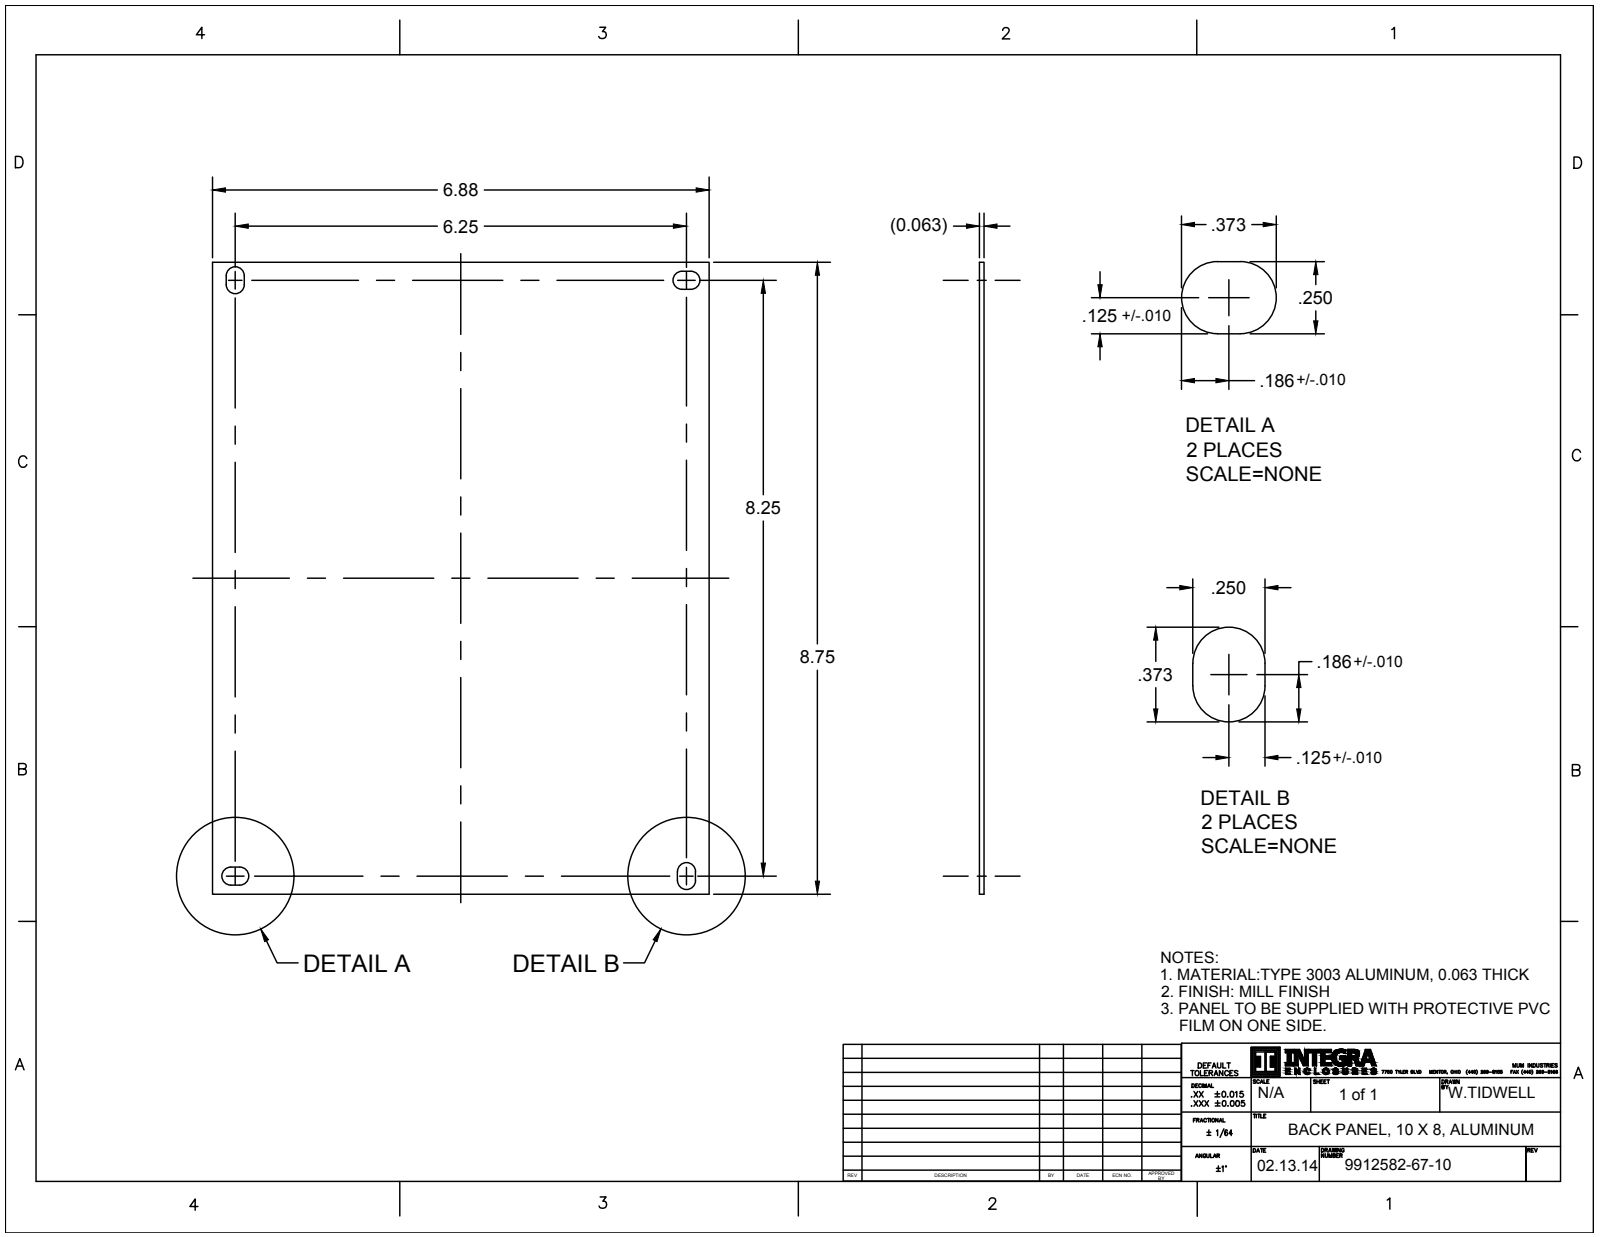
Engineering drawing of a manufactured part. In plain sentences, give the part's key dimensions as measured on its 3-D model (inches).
The part is named "9912582-67-10; 9912518-82-10; ABP108_ASM". Its 3-D file was written by "CREO PARAMETRIC BY PTC INC, 2016050 (CONFIG_CONTROL_DESIGN)". It is 5 solids with 430 faces: 90 planar, 268 cylindrical and 72 other. Overall it measures 8.75 by 6.88 by 0.443 inches. Its volume is 3.84 cubic inches and its surface area 124.5 square inches. Round bosses or shafts: 4 of diameter 0.373, 4 of diameter 0.19, 4 of diameter 0.149. Partial cylindrical surfaces (rounded edges, fillets, slot ends): 48 of radius 0.004, 8 of radius 0.125. The main face-to-face distances are 0.063, 6.88, 8.75, 0.25, 0.313, 0.25, 6.225, 8.217, 0.333, 0.083.
